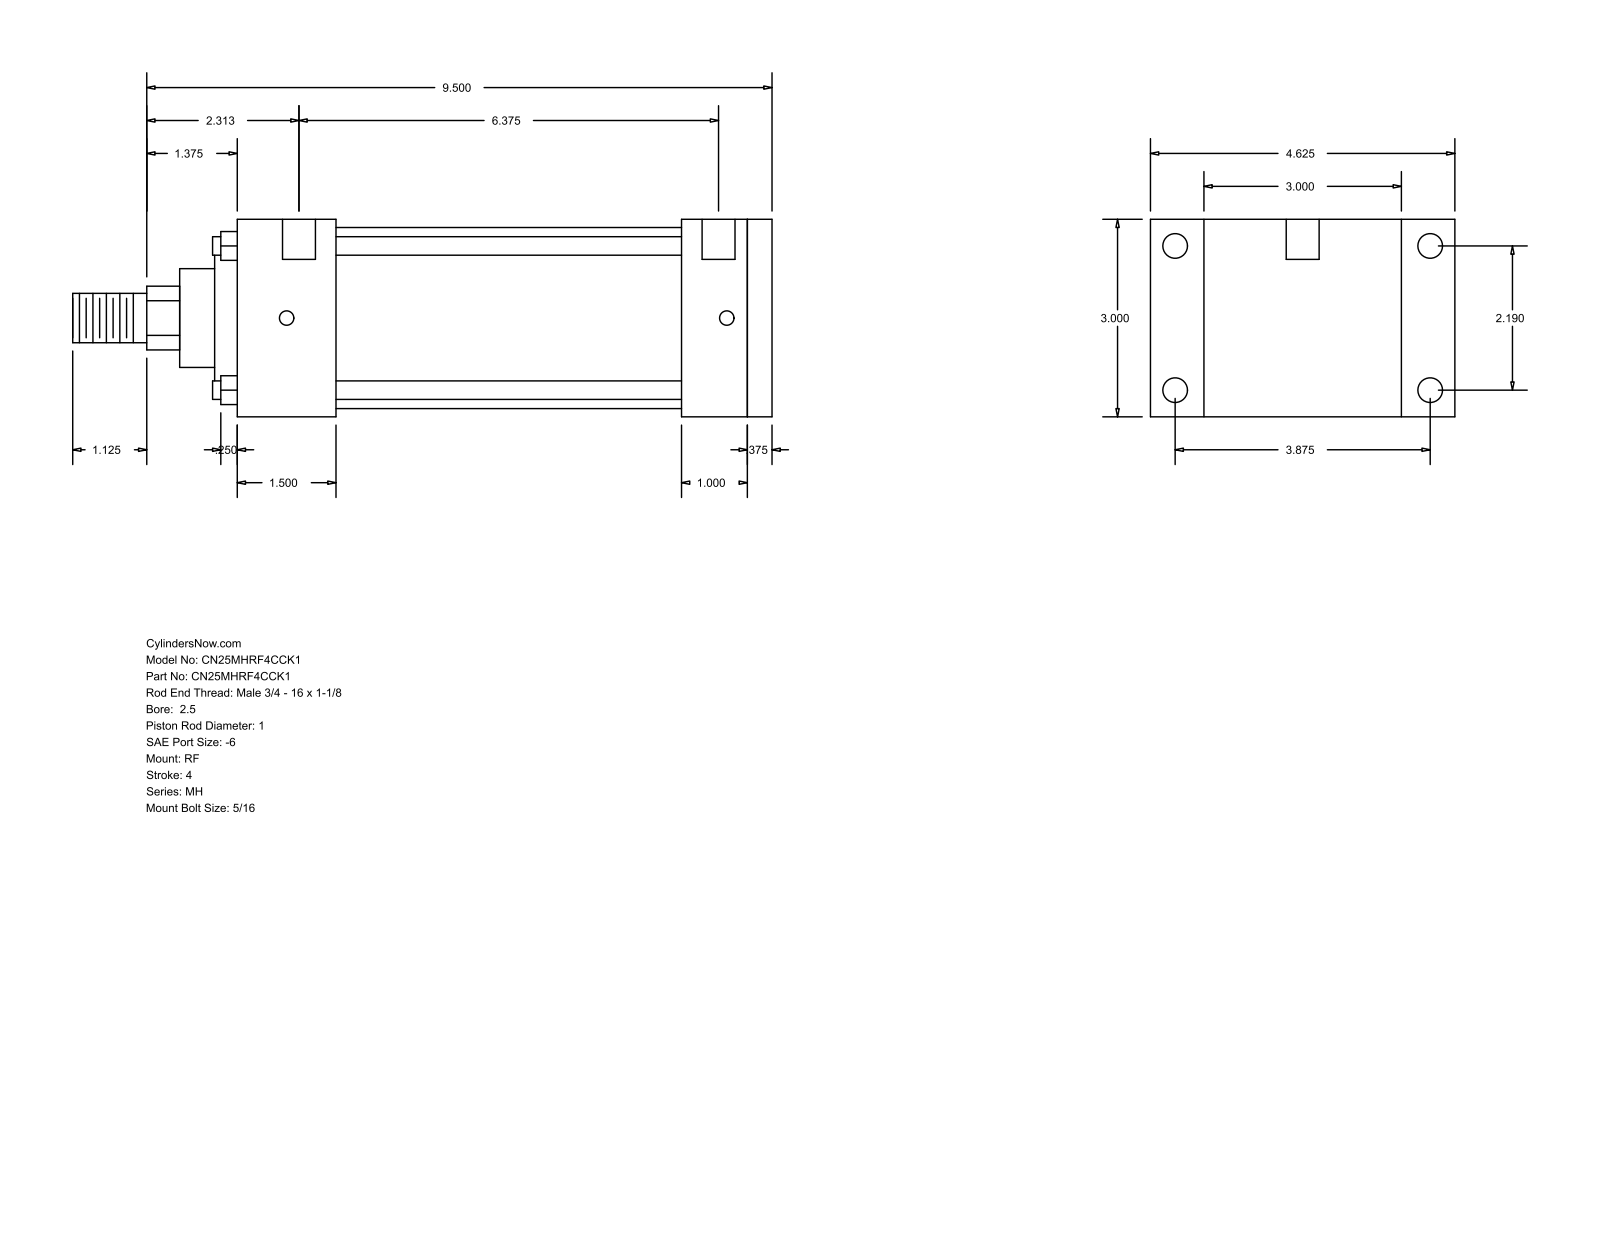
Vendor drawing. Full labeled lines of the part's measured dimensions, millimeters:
Part name (STEP PRODUCT): MH_RF__0250_1
STEP written by: GSSL Pune (CONFIG_CONTROL_DESIGN)
Units: millimetres
Bodies: 0 solids, 94 faces (65 planar, 29 cylindrical, 0 other)
Overall size (bounding box): 269.88 × 117.47 × 76.2
Round holes (diameter × count): ⌀5.56 ×4, ⌀9.53 ×4, ⌀12.7 ×2
Round bosses / shafts (diameter × count): ⌀7.14 ×4, ⌀69.85 ×1, ⌀60.33 ×1, ⌀38.1 ×1, ⌀25.4 ×1, ⌀19.05 ×1
Partial cylindrical surfaces — rounded edges, fillets, slot ends (radius × count): R12.29 ×1
Main face-to-face distances: 76.2, 9.52, 206.38, 196.86, 25.4, 34.92, 171.46, 38.11, 133.35, 158.75
Hole centre spacings: 55.62, 98.42, 113.05, 169.86, 3.18, 4.76, 161.92, 165.1
